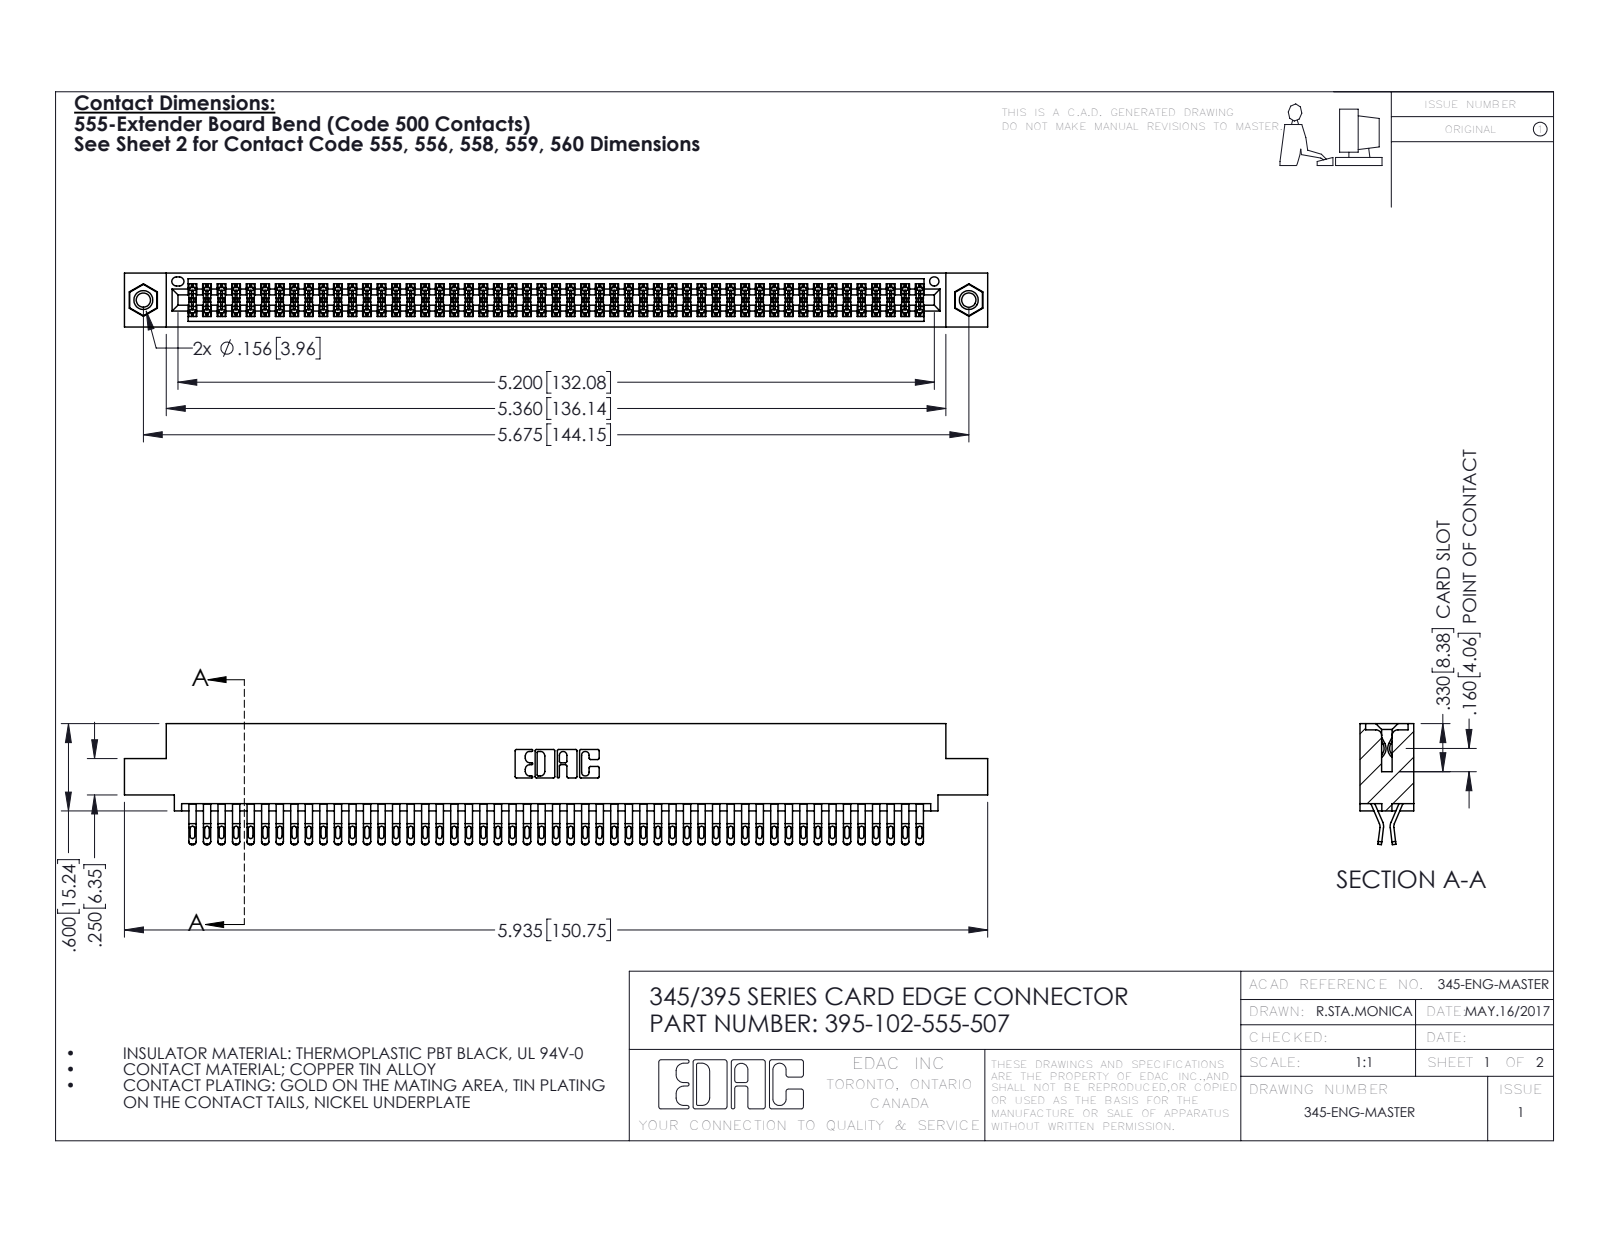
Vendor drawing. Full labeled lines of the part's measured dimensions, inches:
Part name (STEP PRODUCT): 345-250-001_345-250-005-103; 345-292-001_555 Tail; 395-102-555-507; 345 Part_0.110 Offset - 0.156 Dia-TI
STEP written by: SolidWorks 2016 (CONFIG_CONTROL_DESIGN)
Units: inches
Bodies: 105 solids, 5902 faces (3278 planar, 2608 cylindrical, 16 other)
Overall size (bounding box): 5.935 × 0.832 × 0.37
Volume: 0.911 in³ · Surface area: 36.27 in²
Round holes (diameter × count): ⌀0.098 ×2, ⌀0.125 ×2, ⌀0.156 ×2, ⌀0.064 ×1
Round bosses / shafts (diameter × count): ⌀0.155 ×2
Partial cylindrical surfaces — rounded edges, fillets, slot ends (radius × count): R0.016 ×255, R0.02 ×204, R0.006 ×153, R0.01 ×22, R0.007 ×6, R0.031 ×6, R0.026 ×3, R0.01 ×2
Main face-to-face distances: 0.072, 0.298, 0.025, 0.37, 0.2, 0.098, 0.272, 0.225, 0.175, 0.149
Hole centre spacings: 0.27, 5.439, 5.675
